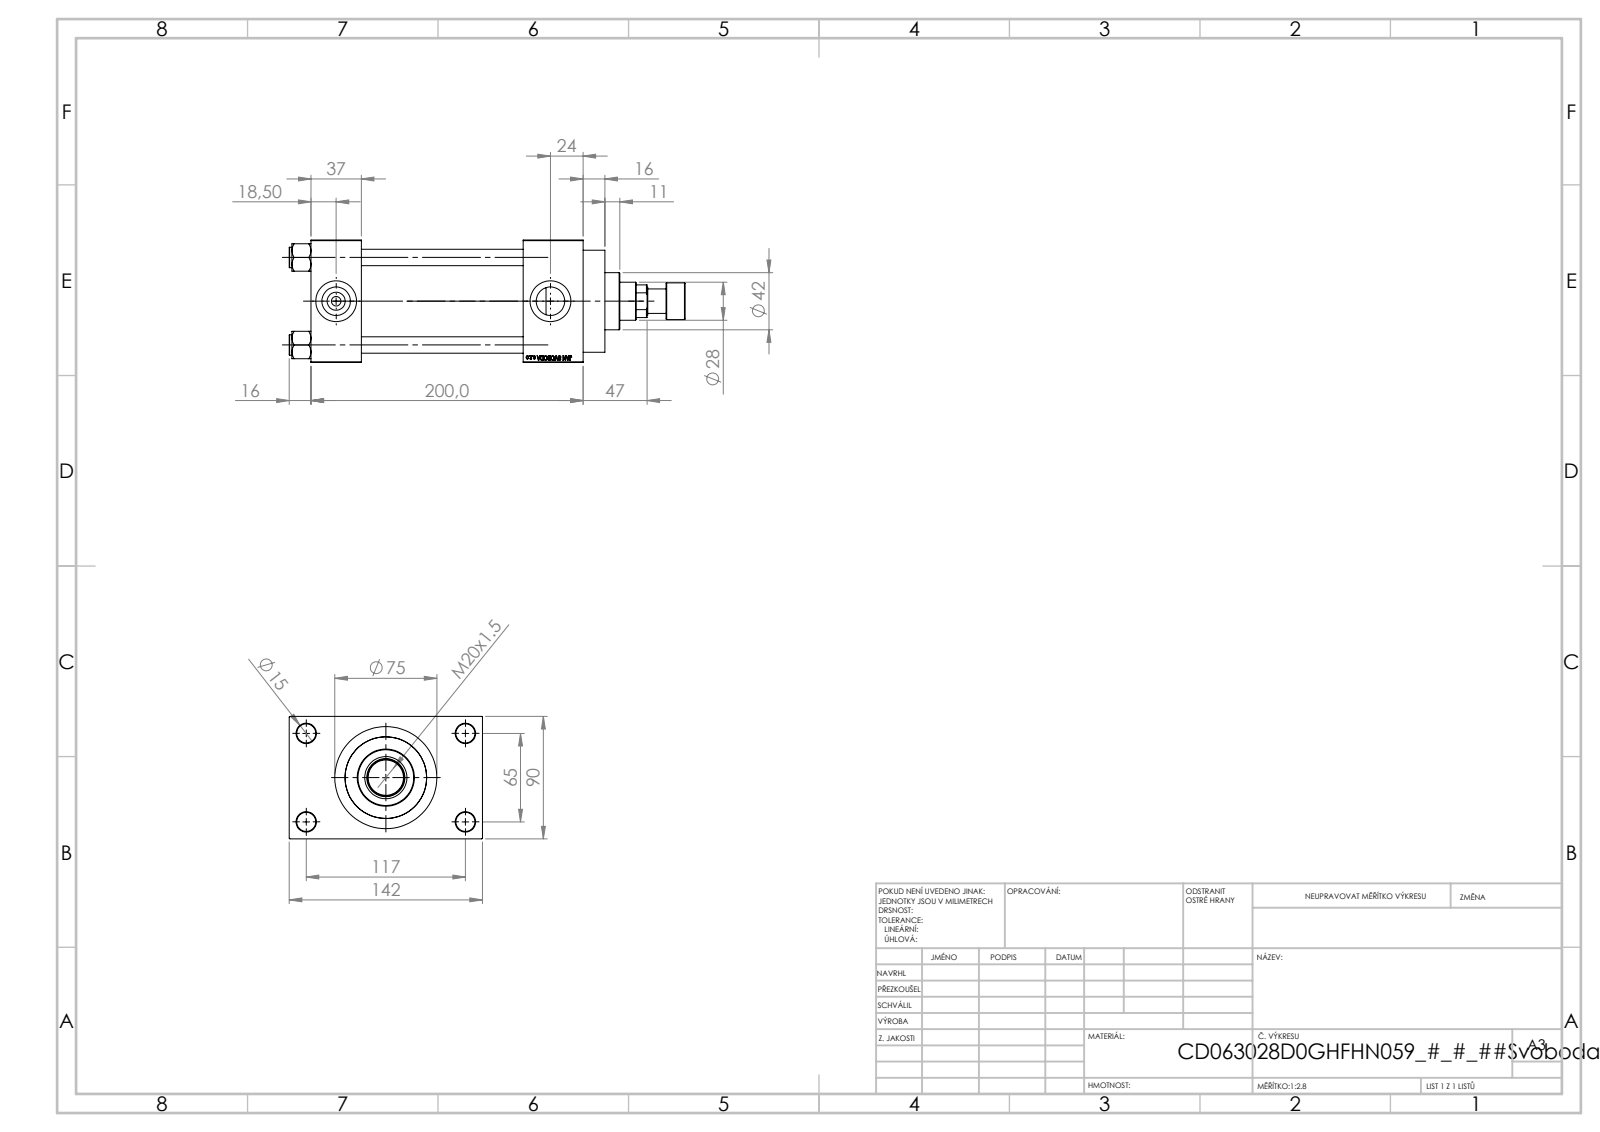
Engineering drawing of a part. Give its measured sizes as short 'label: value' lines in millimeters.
name: V215CD_NUT_M5_D; V215CD_VC_A; V215CD_VCP_D; V215CR_ROD_END_F (+2 more)
written by: SolidWorks 2019 (CONFIG_CONTROL_DESIGN)
unit: mm
bodies: 12 solids, 1117 faces (501 planar, 92 cylindrical, 524 other)
size: 291 × 142 × 90
volume: 1 209 000 mm³; area: 242 777 mm²
holes: 4× ⌀12, 4× ⌀14, 2× ⌀7, 2× ⌀20.96, 2× ⌀30, 1× ⌀18.5, 1× ⌀28, 1× ⌀31, 1× ⌀50, 1× ⌀60, 1× ⌀63
bosses: 4× ⌀15, 1× ⌀75, 1× ⌀69, 1× ⌀42, 1× ⌀27, 1× ⌀18
face distances: 90, 119, 37, 156, 163, 200, 44, 26, 116, 16
hole spacings: 26.35, 45.47, 64.3, 66.92, 69.81, 90.65, 111.34, 65
